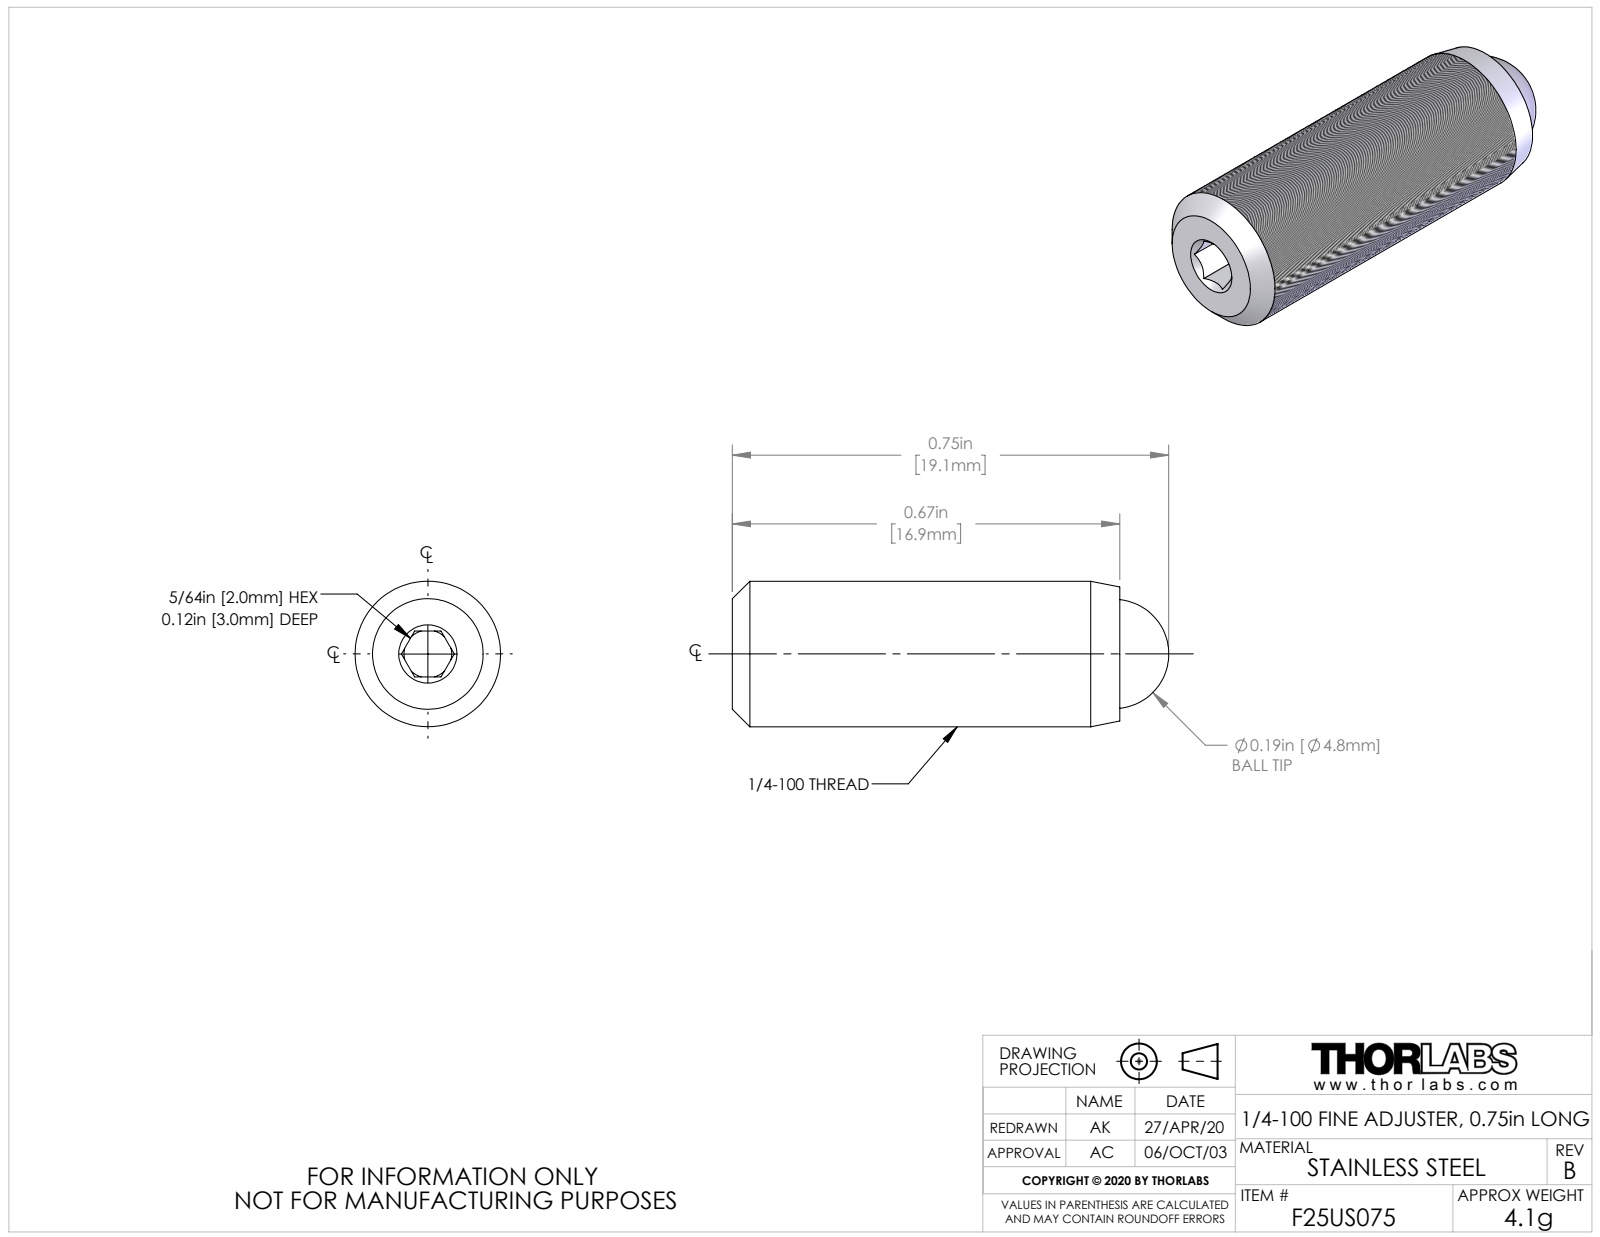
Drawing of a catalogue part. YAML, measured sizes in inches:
part_name: "7642-E0W"
step_written_by: "SolidWorks 2018 (AUTOMOTIVE_DESIGN)"
units: inches
bodies: {solids: 2, faces: 38, planar: 20, cylindrical: 6, other: 12}
overall_size: [0.75, 0.25, 0.25]
volume: 0.033
surface_area: 0.79
round_holes:
  - {diameter: 0.082, count: 1}
  - {diameter: 0.188, count: 1}
round_bosses_or_shafts:
  - {diameter: 0.25, count: 1}
face_to_face_distances: [0.079, 0.666, 0.546, 0.12]
